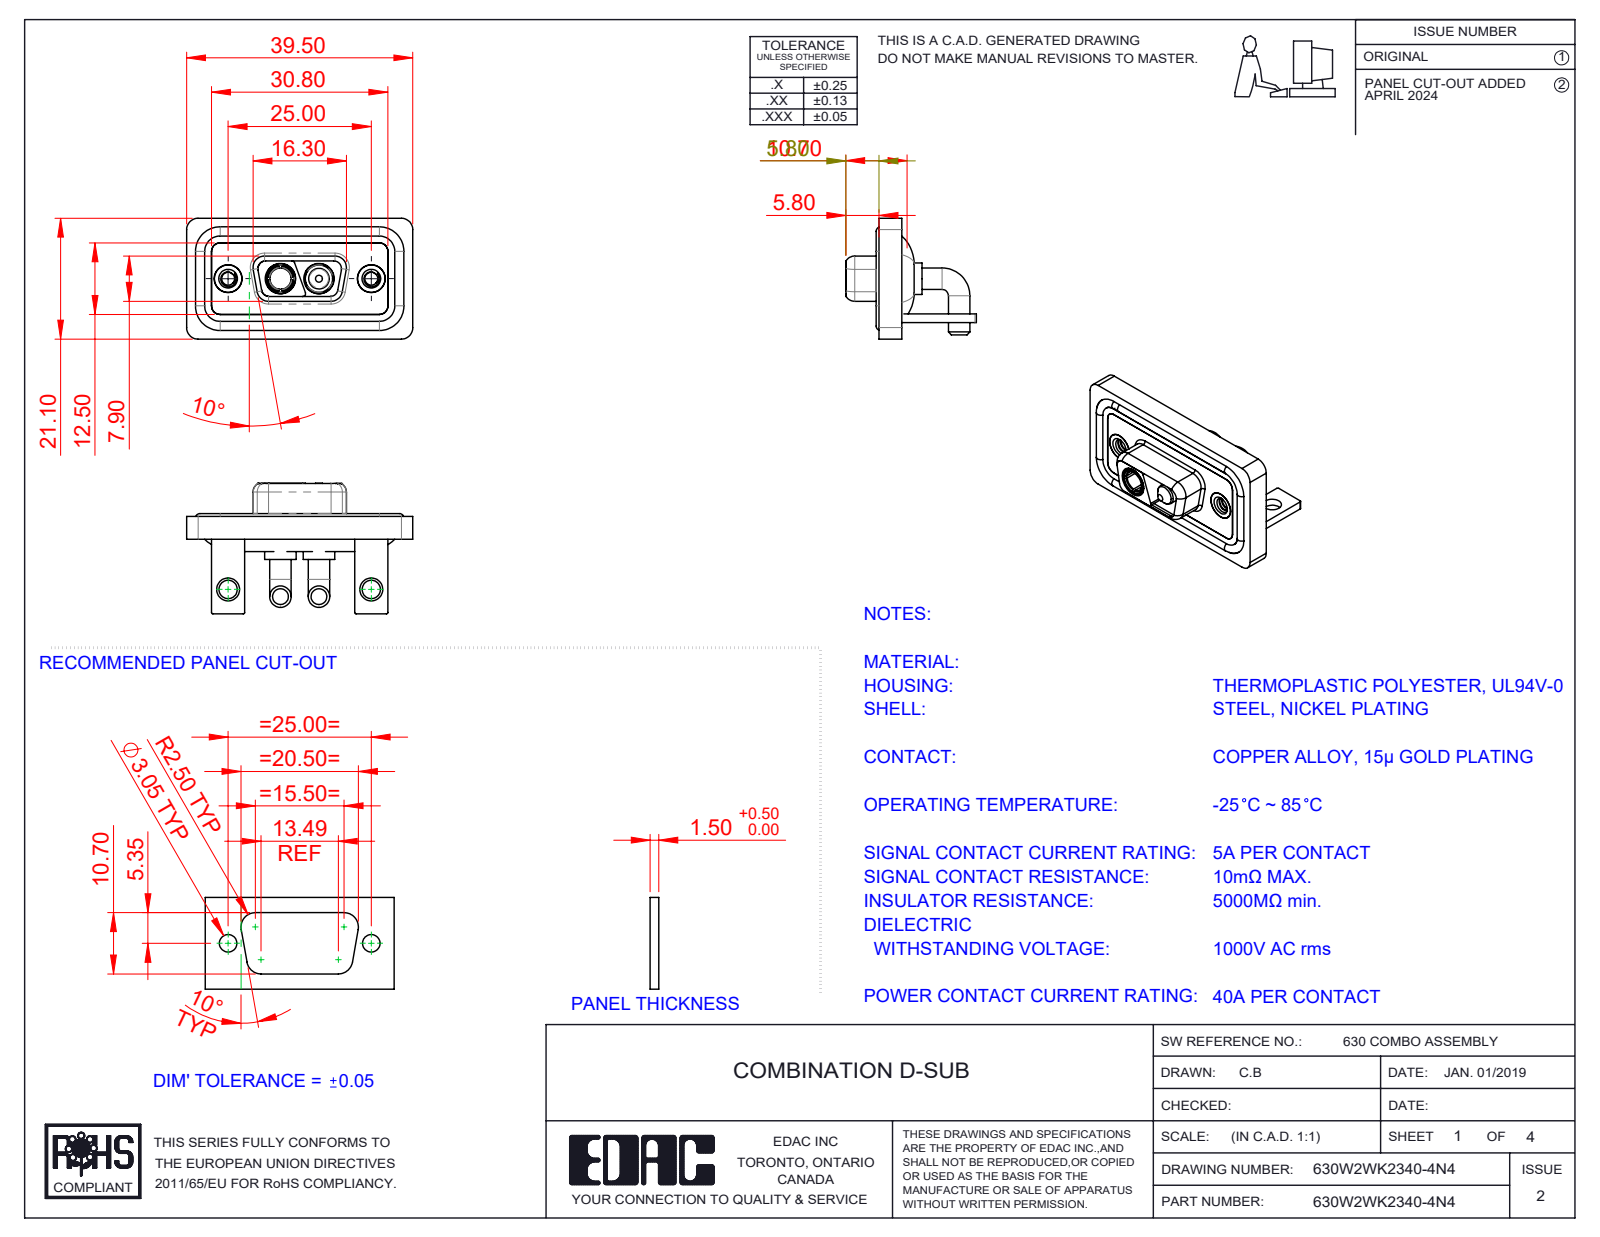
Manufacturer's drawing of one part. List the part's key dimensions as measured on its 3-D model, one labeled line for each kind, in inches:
Part name (STEP PRODUCT): 630Combo Housing_2WK2; 630Combo Threaded Rivet_2; Power Pin_40A RA; 630Combo Shell Front_09 Contacts (+5 more)
STEP written by: SolidWorks 2023 (CONFIG_CONTROL_DESIGN)
Units: inches
Bodies: 13 solids, 556 faces (164 planar, 259 cylindrical, 133 other)
Overall size (bounding box): 1.555 × 0.898 × 0.831
Volume: 0.318 in³ · Surface area: 12.89 in²
Round holes (diameter × count): ⌀0.191 ×4, ⌀0.089 ×2, ⌀0.126 ×2, ⌀0.157 ×2, ⌀0.159 ×2, ⌀0.197 ×2, ⌀0.209 ×2, ⌀0.146 ×1
Round bosses / shafts (diameter × count): ⌀0.148 ×4, ⌀0.063 ×4, ⌀0.217 ×2, ⌀0.205 ×2, ⌀0.195 ×2, ⌀0.189 ×2, ⌀0.187 ×2, ⌀0.195 ×1
Partial cylindrical surfaces — rounded edges, fillets, slot ends (radius × count): R0.079 ×19, R0.059 ×18, R0.01 ×16, R0.053 ×8, R0.063 ×8, R0.02 ×7, R0.024 ×4, R0.026 ×4
Main face-to-face distances: 0.016, 0.114, 0.059, 0.043, 0.146, 0.071, 0.031, 0.098, 0.063, 0.122
Hole centre spacings: 0.36, 0.624, 0.984, 0.265
